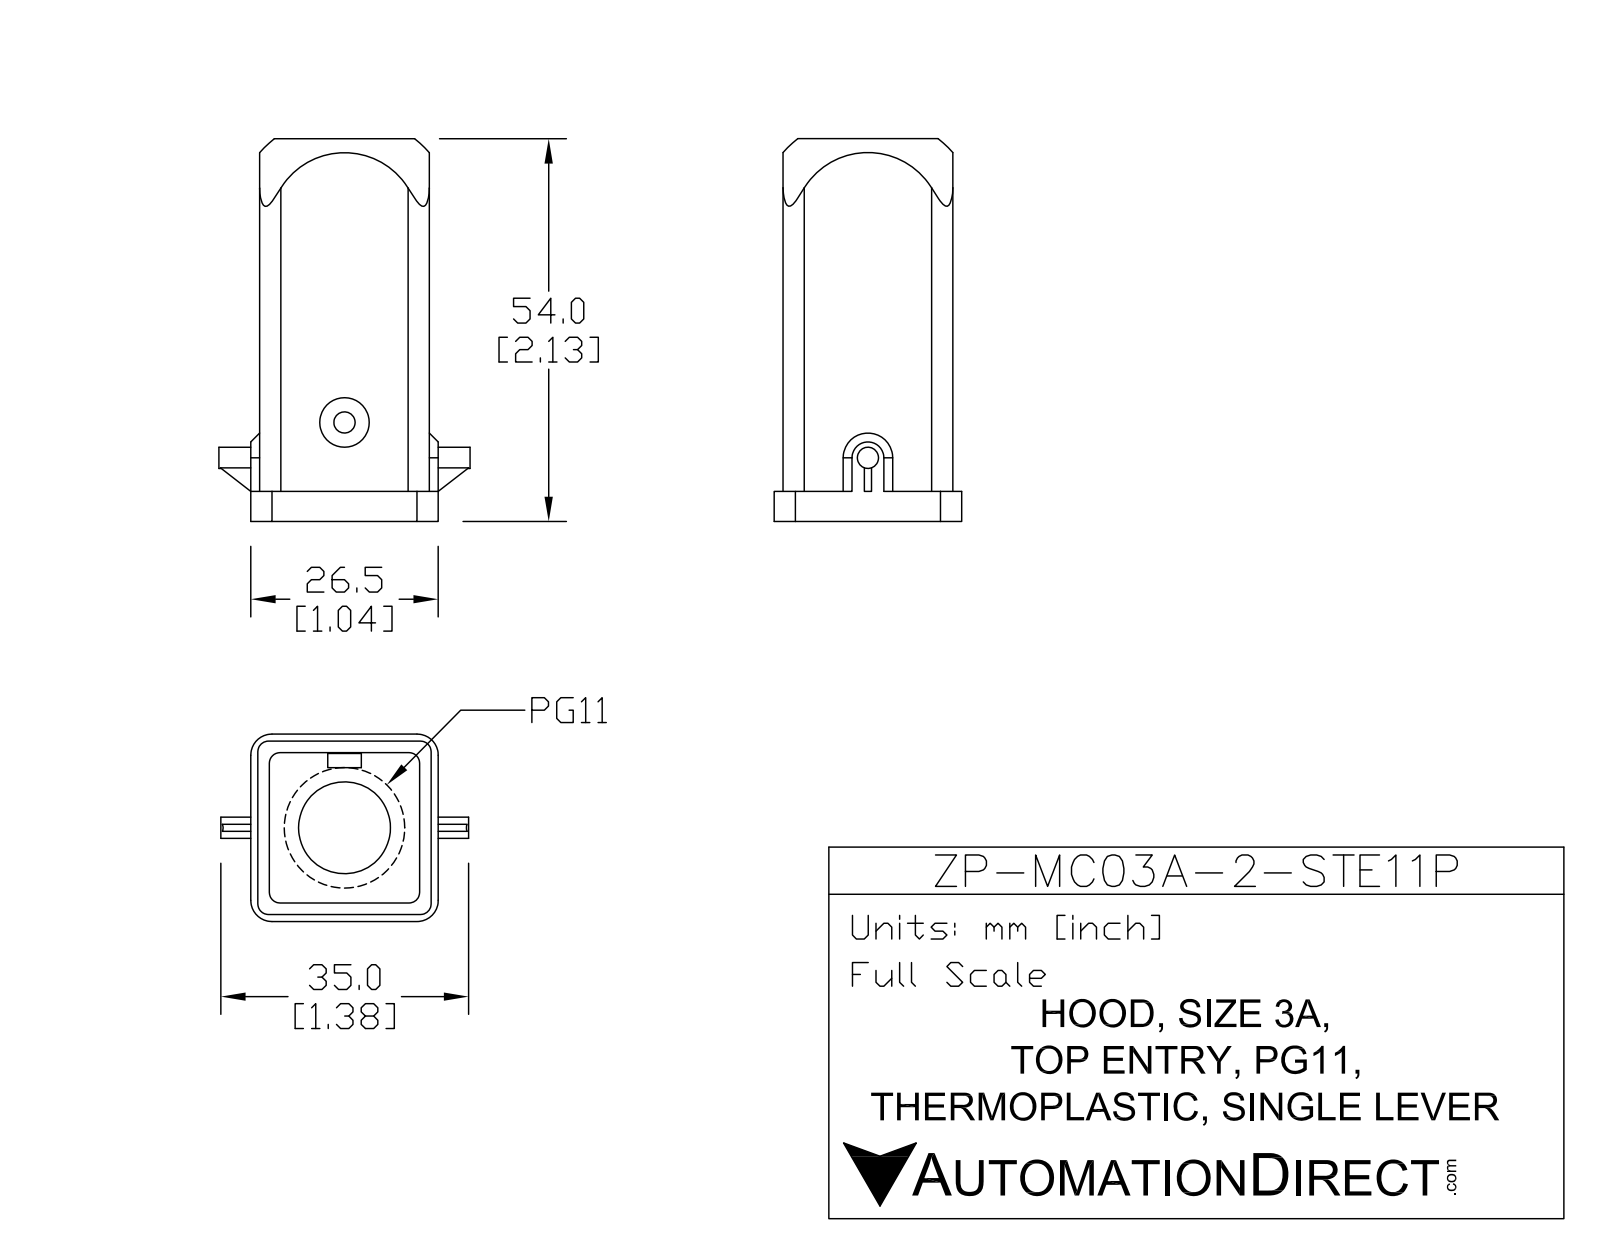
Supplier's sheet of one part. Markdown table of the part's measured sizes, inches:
| quantity | value |
| --- | --- |
| part name | ZP-MC03A-2-STE11P |
| STEP written by | SolidWorks 2011 (AUTOMOTIVE_DESIGN) |
| units | inches |
| bodies | 1 solid, 65 faces (40 planar, 21 cylindrical, 4 other) |
| overall size | 2.122 × 1.398 × 1.043 |
| volume | 0.568 in³ |
| surface area | 15.75 in² |
| round holes (diameter × count) | 0.118 × 1, 0.512 × 1, 0.669 × 1 |
| round bosses / shafts (diameter × count) | 0.118 × 1 |
| partial cylindrical surfaces (radius × count) | 0.059 × 8, 0.118 × 8 |
| main face-to-face distances | 0.054, 0.891, 0.945, 0.837, 0.049, 0.103, 0.94, 0.994, 0.039, 1.004 |
